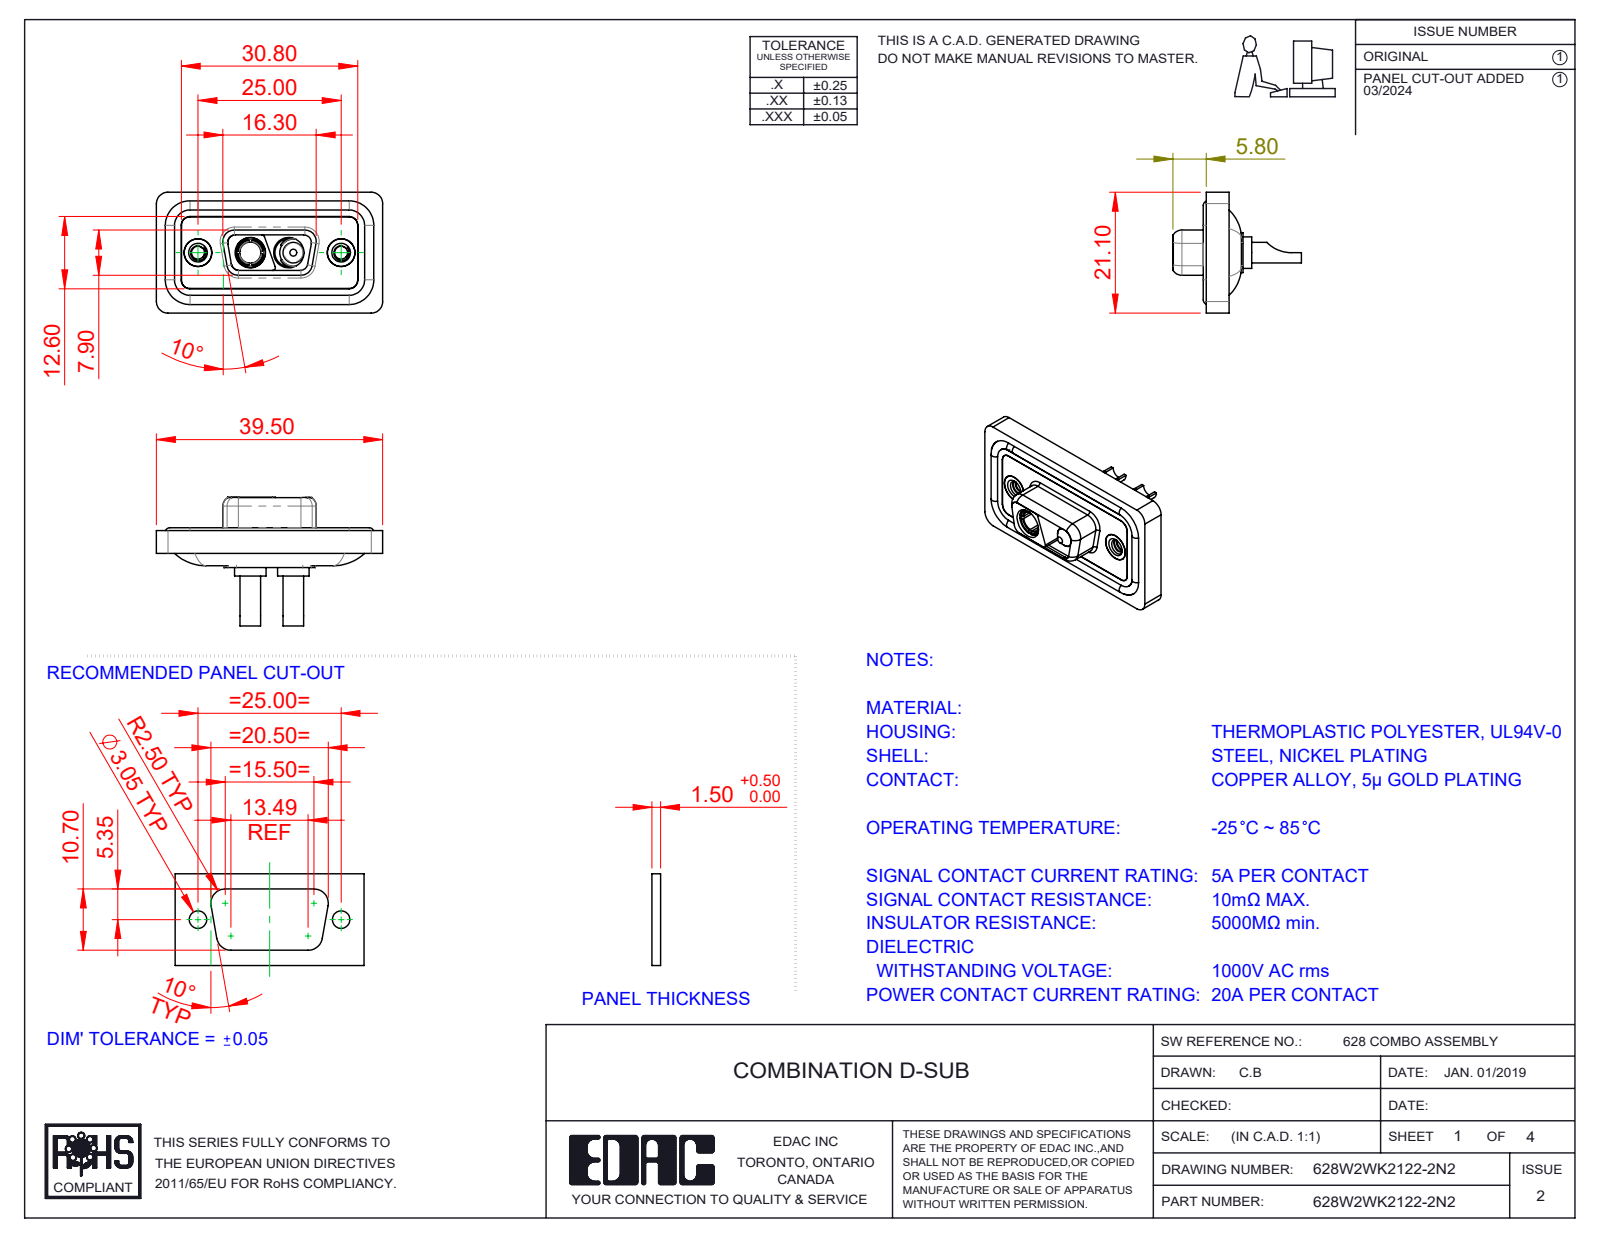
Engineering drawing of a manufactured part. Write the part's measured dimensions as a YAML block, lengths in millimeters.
part_name: "628Combo Threaded Rivet_2; Power Socket_20A SC; Power Pin_20A SC; 628Combo Waterproof Housing_09 Contacts (+4 more)"
step_written_by: "SolidWorks 2023 (CONFIG_CONTROL_DESIGN)"
units: millimeters
bodies: {solids: 11, faces: 512, planar: 150, cylindrical: 237, other: 125}
overall_size: [39.5, 22.45, 21.1]
volume: 4629
surface_area: 7509
round_holes:
  - {diameter: 4.85, count: 4}
  - {diameter: 2.26, count: 2}
  - {diameter: 2.7, count: 2}
  - {diameter: 4, count: 2}
  - {diameter: 4.05, count: 2}
  - {diameter: 5, count: 2}
  - {diameter: 5.3, count: 2}
  - {diameter: 3.7, count: 1}
round_bosses_or_shafts:
  - {diameter: 1.6, count: 4}
  - {diameter: 5.5, count: 2}
  - {diameter: 5.2, count: 2}
  - {diameter: 4.95, count: 2}
  - {diameter: 4.8, count: 2}
  - {diameter: 4.75, count: 2}
  - {diameter: 3.75, count: 2}
  - {diameter: 3.6, count: 2}
partial_cylinders:
  - {radius: 1.5, count: 22}
  - {radius: 2, count: 18}
  - {radius: 1.35, count: 8}
  - {radius: 1.6, count: 8}
  - {radius: 0.5, count: 6}
  - {radius: 0.25, count: 4}
  - {radius: 0.6, count: 4}
  - {radius: 0.65, count: 4}
face_to_face_distances: [0.4, 1.1, 2.9, 1.6, 0.5, 1.8, 5.65, 1.5, 5.35, 3.1]
hole_center_spacings: [9.14, 15.86, 6.72, 25]
